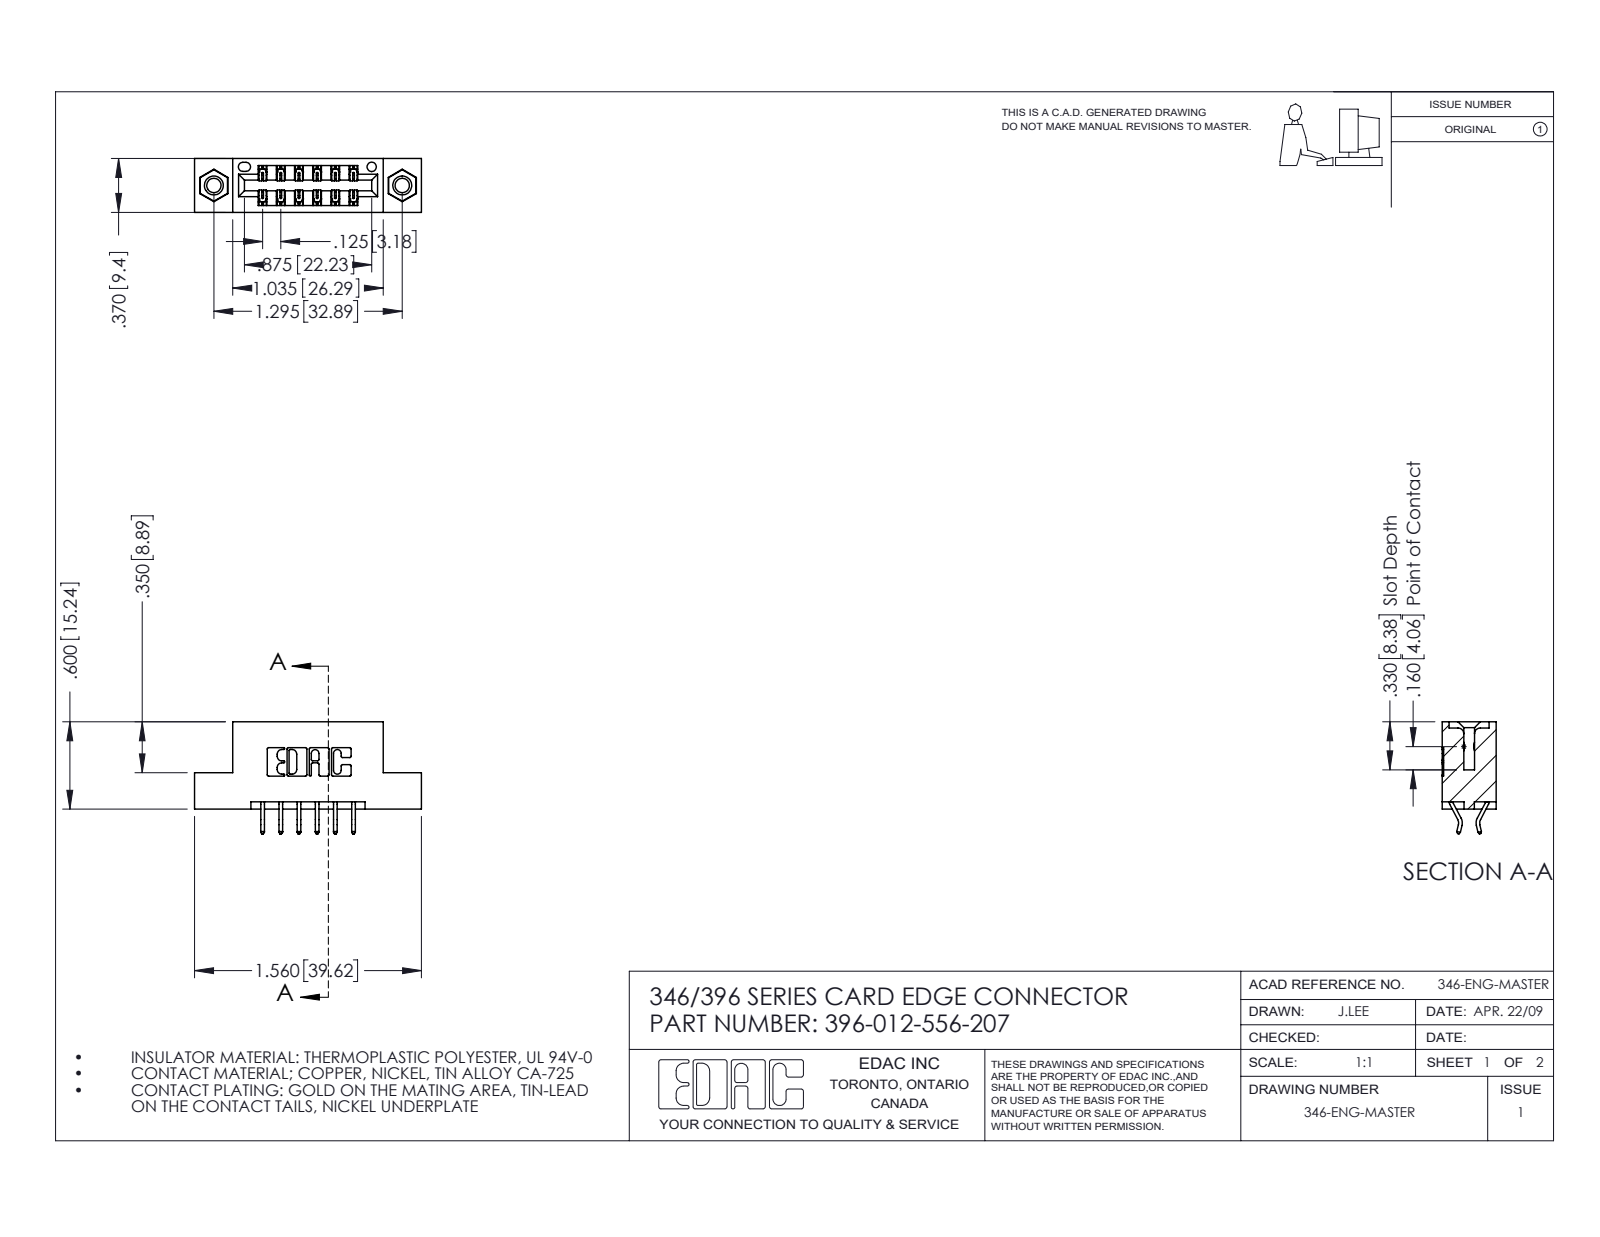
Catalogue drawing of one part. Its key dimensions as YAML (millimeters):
part_name: "396-012-556-207; 346 Part_Flush Mounting Lugs - 0.156 Dia-TI; 345-250-001_345-250-005-103; 345-292-001_556 Tail"
step_written_by: "SolidWorks 2016 (CONFIG_CONTROL_DESIGN)"
units: millimeters
bodies: {solids: 15, faces: 878, planar: 576, cylindrical: 286, other: 16}
overall_size: [39.6, 19.6, 9.4]
volume: 3570
surface_area: 4365
round_holes:
  - {diameter: 2.5, count: 2}
  - {diameter: 3.2, count: 2}
  - {diameter: 4, count: 2}
  - {diameter: 1.6, count: 1}
round_bosses_or_shafts:
  - {diameter: 3.9, count: 2}
partial_cylinders:
  - {radius: 0.3, count: 22}
  - {radius: 0.2, count: 18}
  - {radius: 0.2, count: 6}
  - {radius: 0.8, count: 6}
  - {radius: 0.7, count: 3}
  - {radius: 0.3, count: 2}
  - {radius: 0.4, count: 2}
  - {radius: 0.6, count: 2}
face_to_face_distances: [6.4, 9.4, 1.2, 8.2, 3.8, 5.6, 2.5, 4.4, 0.6, 1.8]
hole_center_spacings: [6.2, 27.7, 32.9]
